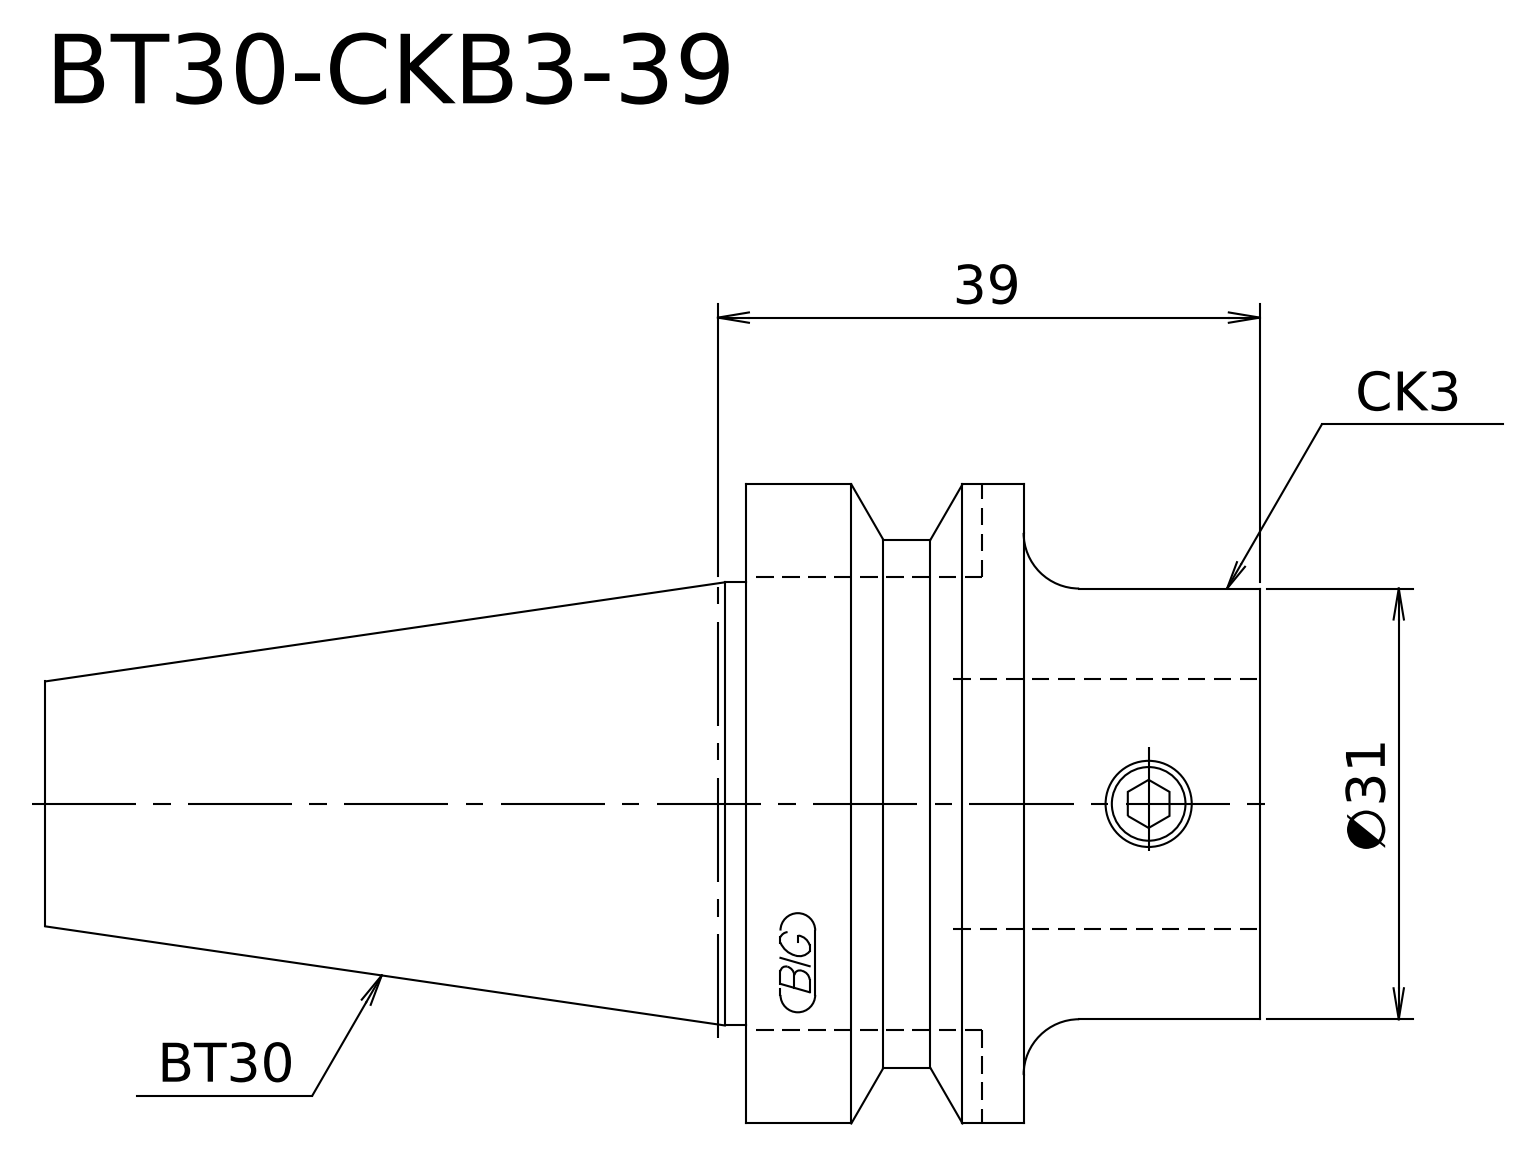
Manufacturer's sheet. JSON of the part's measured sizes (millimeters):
{"step_written_by": "Kubotek KeyCreator V8.5.1 (14335) (CONFIG_CONTROL_DESIGN)", "units": "millimeters", "bodies": {"solids": 1, "faces": 13, "planar": 4, "cylindrical": 5, "other": 4}, "overall_size": [87.4, 46, 46], "volume_mm3": 69778, "surface_area_mm2": 11524, "round_bosses_or_shafts": [[46, 1], [38, 1], [31.9, 1], [31, 1]], "face_to_face_distances": [37, 17, 20, 87.4, 70.4, 50.4]}
